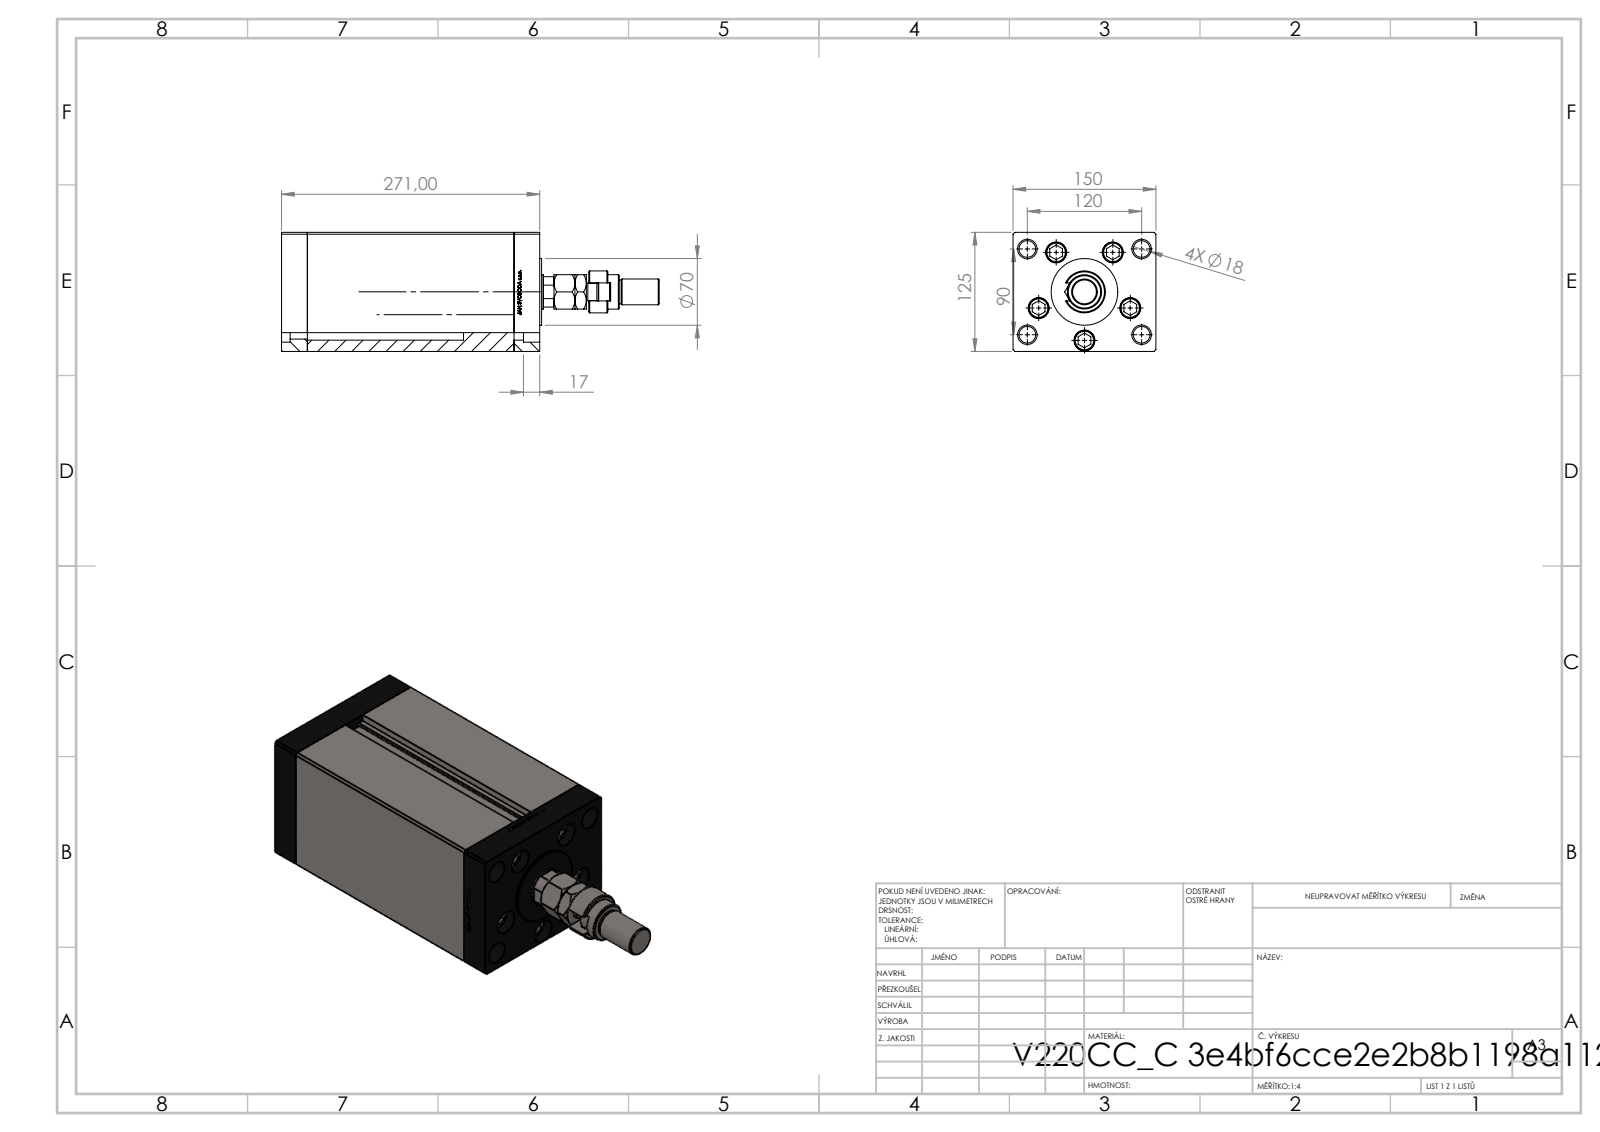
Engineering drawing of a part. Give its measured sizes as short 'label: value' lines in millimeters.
name: V220C_VC_C; V220C BACK_C; ALLEN BOLT; V220C_C MIDDLE (+3 more)
written by: SolidWorks 2019 (CONFIG_CONTROL_DESIGN)
unit: mm
bodies: 15 solids, 1248 faces (570 planar, 172 cylindrical, 506 other)
size: 396.5 × 150 × 125
volume: 4 226 000 mm³; area: 470 985 mm²
holes: 9× ⌀17.5, 5× ⌀22, 4× ⌀16, 4× ⌀20.5, 1× ⌀21, 1× ⌀25.5
bosses: 5× ⌀8, 4× ⌀21, 1× ⌀80, 1× ⌀70, 1× ⌀44, 1× ⌀36, 1× ⌀28, 1× ⌀27
rounds: 2× R0.93, 1× R9.5, 1× R15, 1× R17.5
face distances: 150, 125, 27, 244, 217, 33.5, 6.5, 271, 237.5, 210.5
hole spacings: 51, 75, 30.43, 30.48, 58.89, 60.3, 61.25, 63.14
